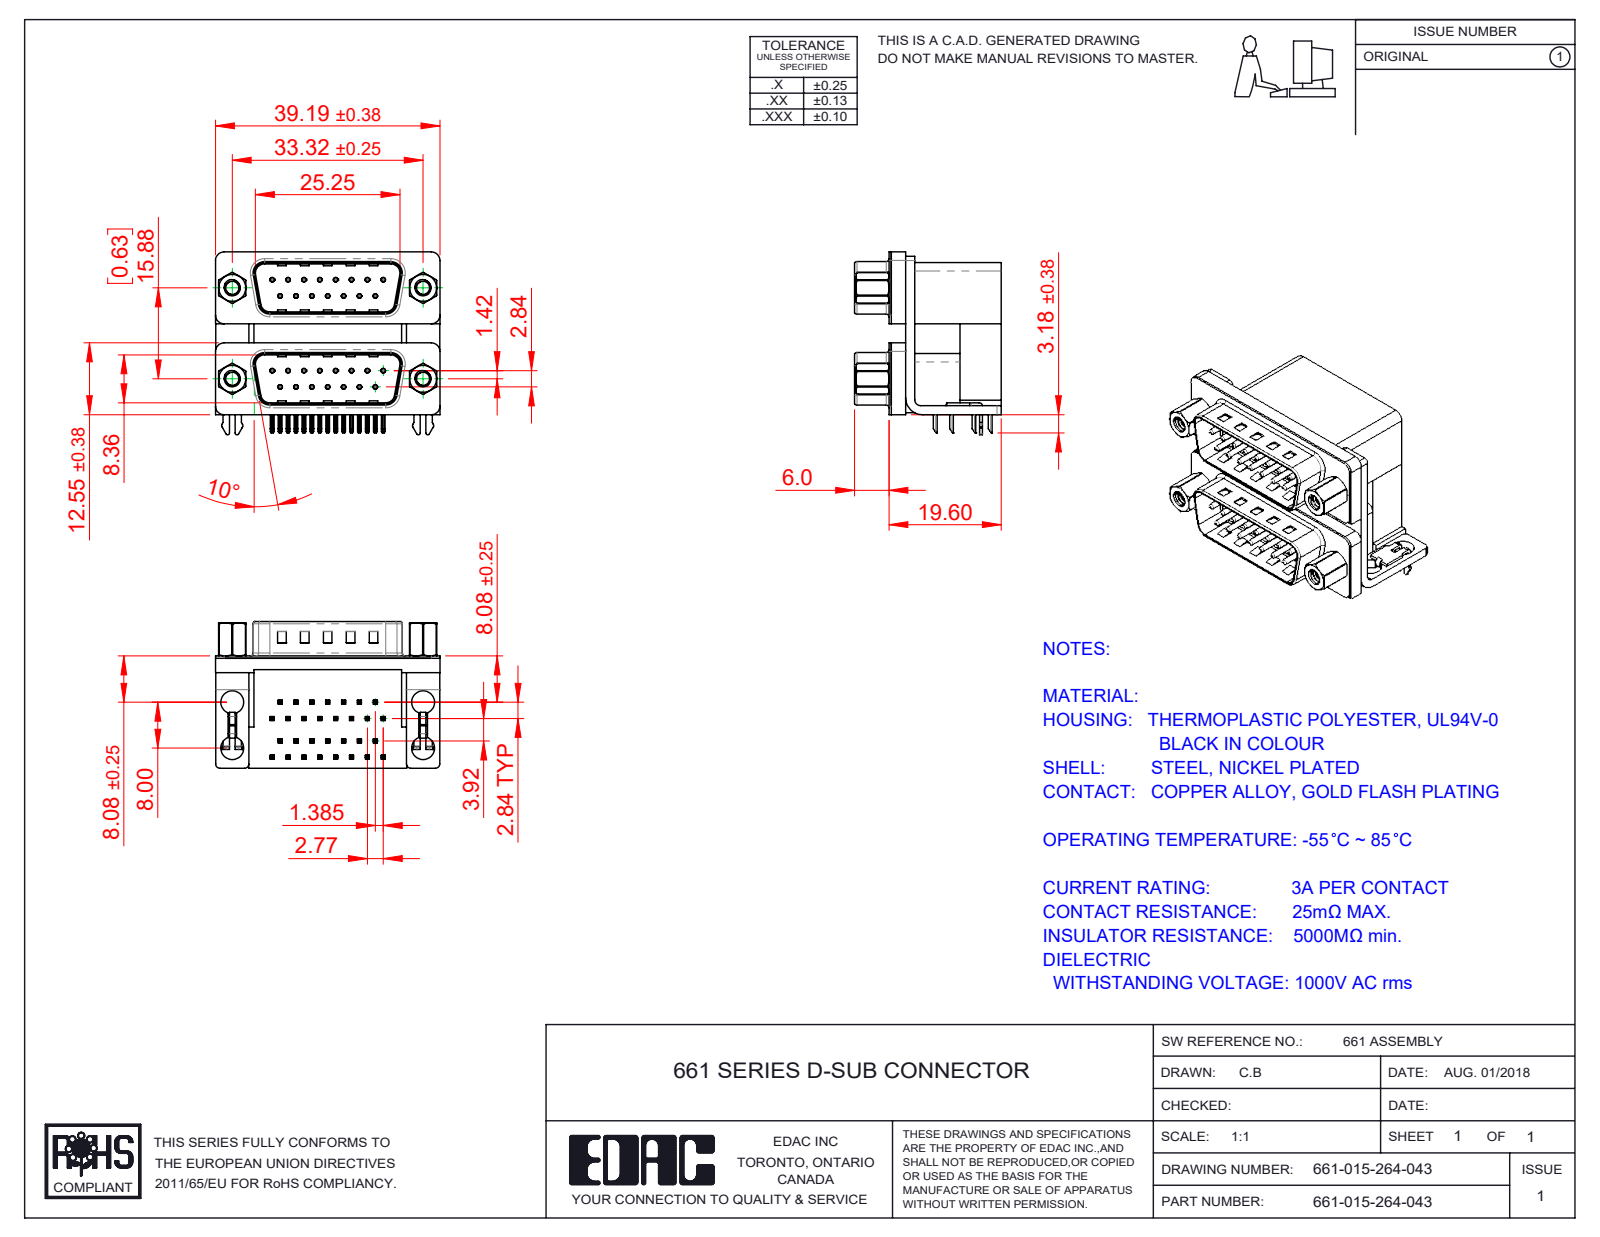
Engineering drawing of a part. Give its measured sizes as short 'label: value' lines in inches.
name: 661 Contact Top Lower; 661 Threaded Rivet_4-40; 661 Mounting Bracket_2ProngL; 661-015-264-043 (+8 more)
written by: SolidWorks 2020 (CONFIG_CONTROL_DESIGN)
unit: in
bodies: 47 solids, 3322 faces (1956 planar, 1028 cylindrical, 338 other)
size: 1.543 × 1.257 × 1.008
volume: 0.865 in³; area: 25.1 in²
holes: 30× ⌀0.014, 30× ⌀0.031, 8× ⌀0.157, 4× ⌀0.089, 4× ⌀0.09, 4× ⌀0.138, 4× ⌀0.189, 4× ⌀0.197
bosses: 30× ⌀0.03, 4× ⌀0.193, 4× ⌀0.187, 4× ⌀0.154, 4× ⌀0.11
rounds: 126× R0.01, 60× R0.005, 20× R0.02, 16× R0.059, 10× R0.03, 8× R0.035, 8× R0.063, 8× R0.079
face distances: 0.016, 0.756, 0.657, 0.098, 0.625, 0.283, 0.472, 0.374, 0.421, 0.114
hole spacings: 0.124, 0.109, 0.635, 0.218, 0.662, 0.327, 0.706, 0.625
